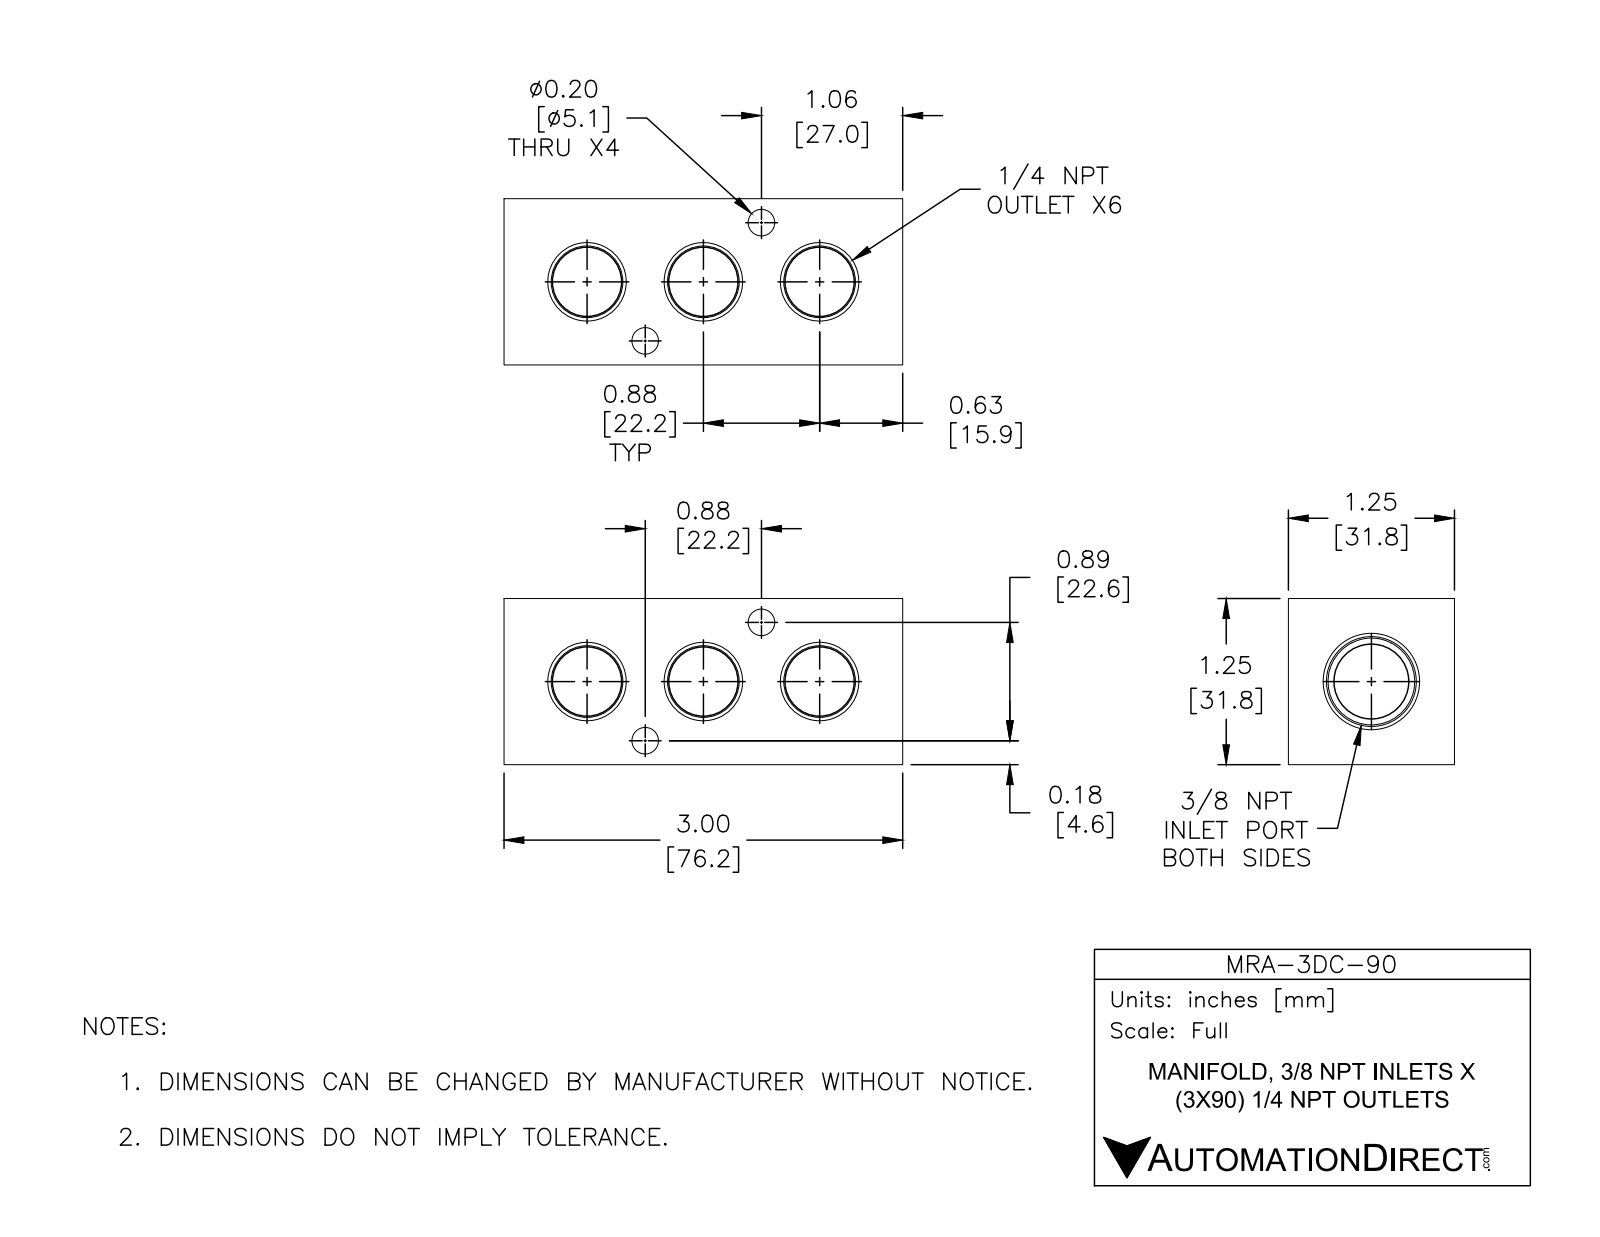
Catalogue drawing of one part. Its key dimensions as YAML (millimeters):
part_name: "MRA-3DC-90"
step_written_by: "SolidWorks 2015 (CONFIG_CONTROL_DESIGN)"
units: millimeters
bodies: {solids: 1, faces: 86, planar: 22, cylindrical: 32, other: 32}
overall_size: [76.2, 31.8, 31.8]
volume: 52830
surface_area: 17370
round_holes:
  - {diameter: 5.1, count: 4}
  - {diameter: 14.3, count: 1}
partial_cylinders:
  - {radius: 5.6, count: 6}
face_to_face_distances: [31.8, 76.2, 21.8, 9.9, 10.4, 65.8, 55.4]
hole_center_spacings: [31.7]
